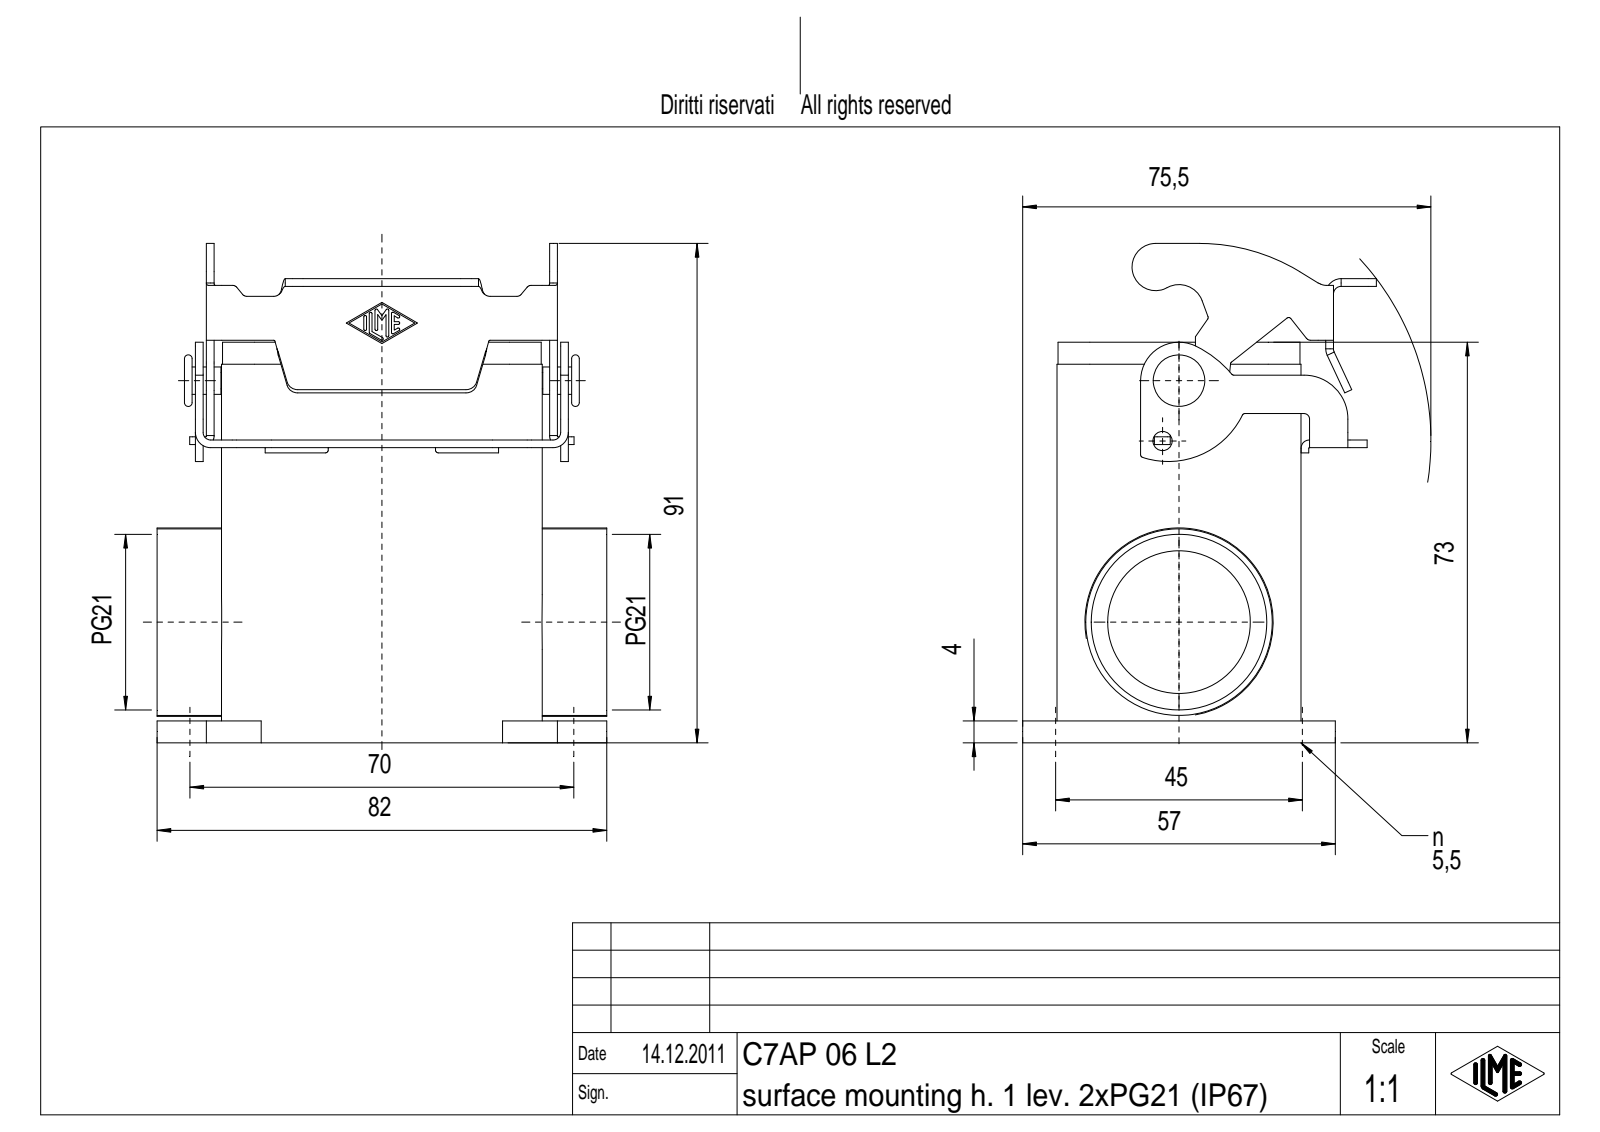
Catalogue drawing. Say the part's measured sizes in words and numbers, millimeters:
The part is named "MSBO10147.1". Its 3-D file was written by "Creo Elements/Direct Modeling 18.0B 02-Dec-2011 (C) Parametric Technology GmbH (AUTOMOTIVE_DESIGN)". It is 1 solid with 403 faces: 205 planar, 176 cylindrical and 22 other. Overall it measures 91 by 82 by 64.48 millimeters. Its volume is 91 883 cubic millimeters and its surface area 47 952 square millimeters. Round holes: 4 of diameter 2.46, 4 of diameter 3, 4 of diameter 5.5, 1 of diameter 24.5, 1 of diameter 26.8. Round bosses or shafts: 1 of diameter 34, 1 of diameter 5, 1 of diameter 3.2, 1 of diameter 3. Partial cylindrical surfaces (rounded edges, fillets, slot ends): 16 of radius 0.25, 12 of radius 0.5, 12 of radius 1, 11 of radius 1.5, 8 of radius 2, 6 of radius 1.4, 6 of radius 2.8, 4 of radius 1.8. The main face-to-face distances are 4, 40.5, 1.4, 44.5, 36.5, 6.75, 10.75, 47.75, 2, 73. The hole center spacings are 15.81, 38.28, 57.71, 67.42, 27, 44, 45, 51.62.
